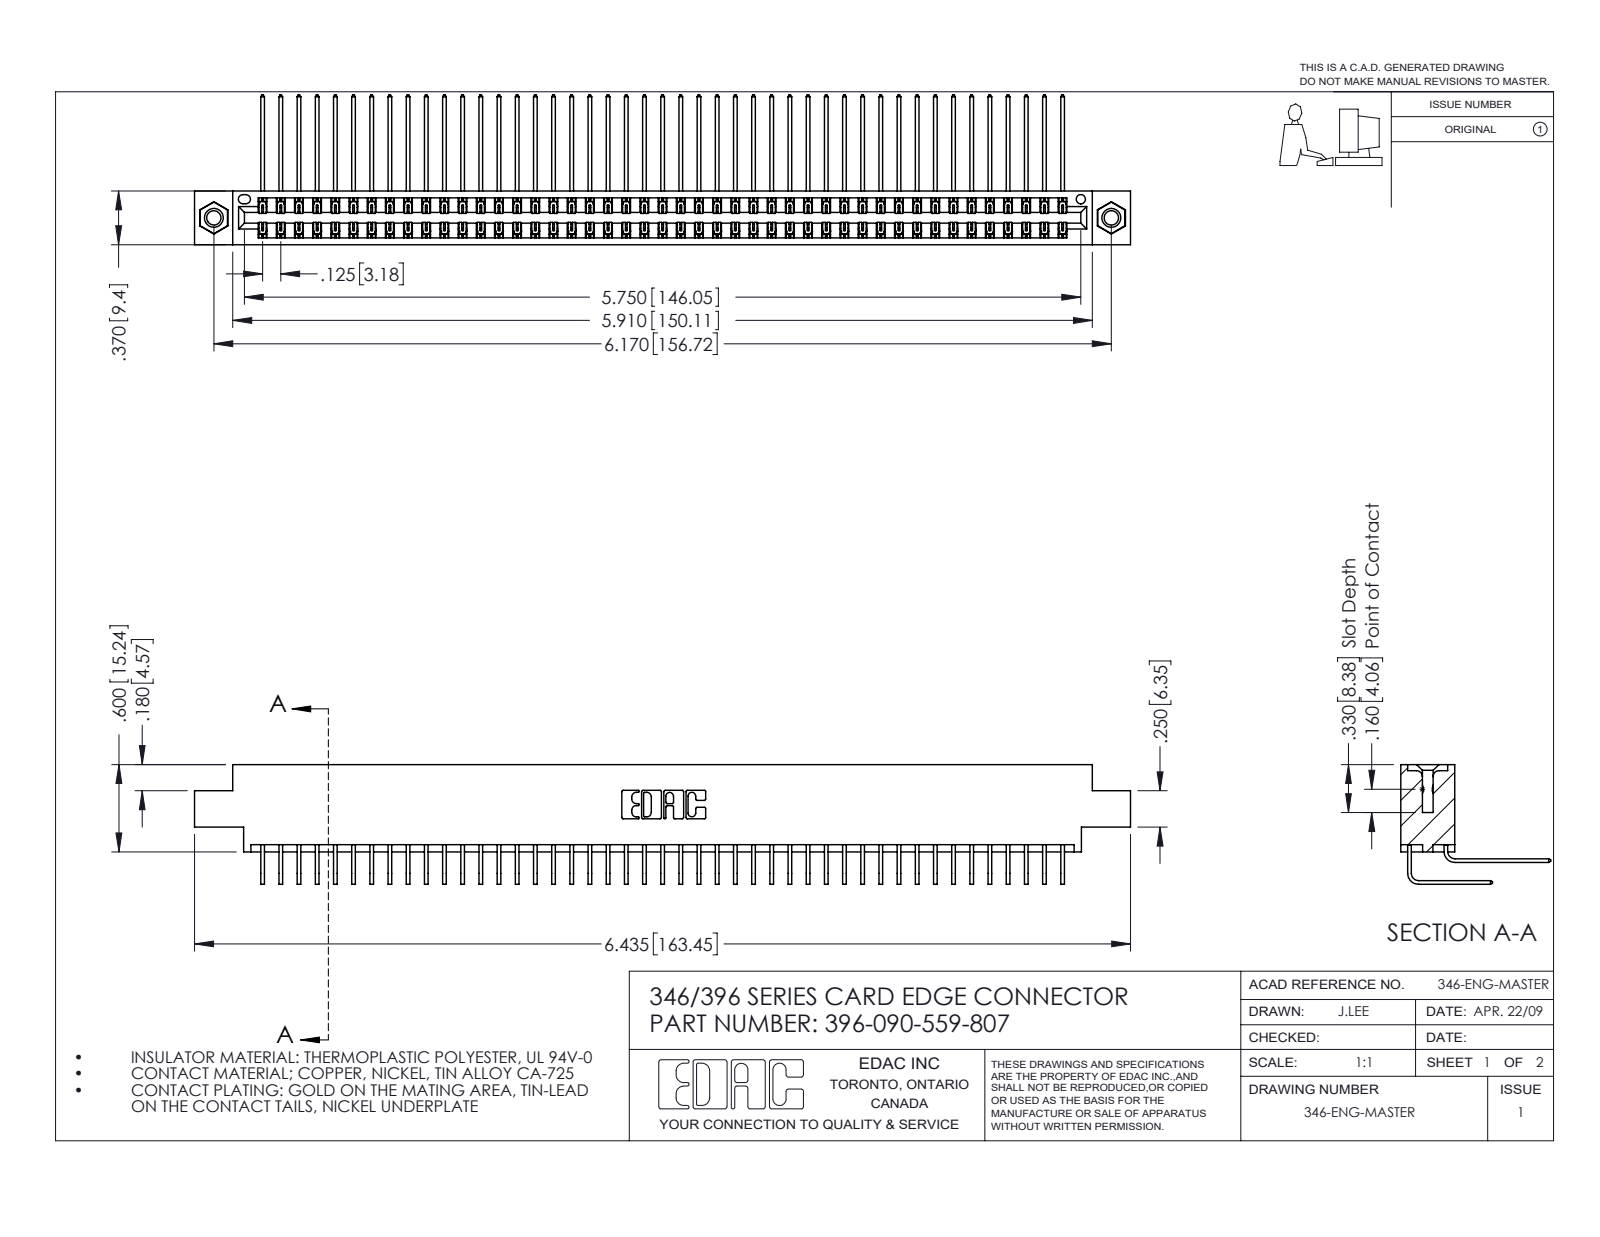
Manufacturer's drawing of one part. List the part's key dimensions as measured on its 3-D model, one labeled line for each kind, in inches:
Part name (STEP PRODUCT): 396-090-559-807; 346 Part_0.170 Offset - 0.156 Dia-TI; 345-250-001_345-250-005-103; 345-292-001_559 Tail - 2 (+1 more)
STEP written by: SolidWorks 2016 (CONFIG_CONTROL_DESIGN)
Units: inches
Bodies: 93 solids, 5046 faces (3442 planar, 1588 cylindrical, 16 other)
Overall size (bounding box): 6.435 × 1.03 × 0.823
Volume: 0.995 in³ · Surface area: 39.02 in²
Round holes (diameter × count): ⌀0.098 ×2, ⌀0.125 ×2, ⌀0.156 ×2, ⌀0.064 ×1
Round bosses / shafts (diameter × count): ⌀0.155 ×2
Partial cylindrical surfaces — rounded edges, fillets, slot ends (radius × count): R0.006 ×135, R0.01 ×22, R0.007 ×6, R0.031 ×6, R0.026 ×3, R0.014 ×2, R0.022 ×2, R0.024 ×2
Main face-to-face distances: 0.048, 0.322, 0.025, 0.37, 0.25, 0.072, 0.298, 0.275, 0.222, 0.148
Hole centre spacings: 0.246, 5.961, 6.17
